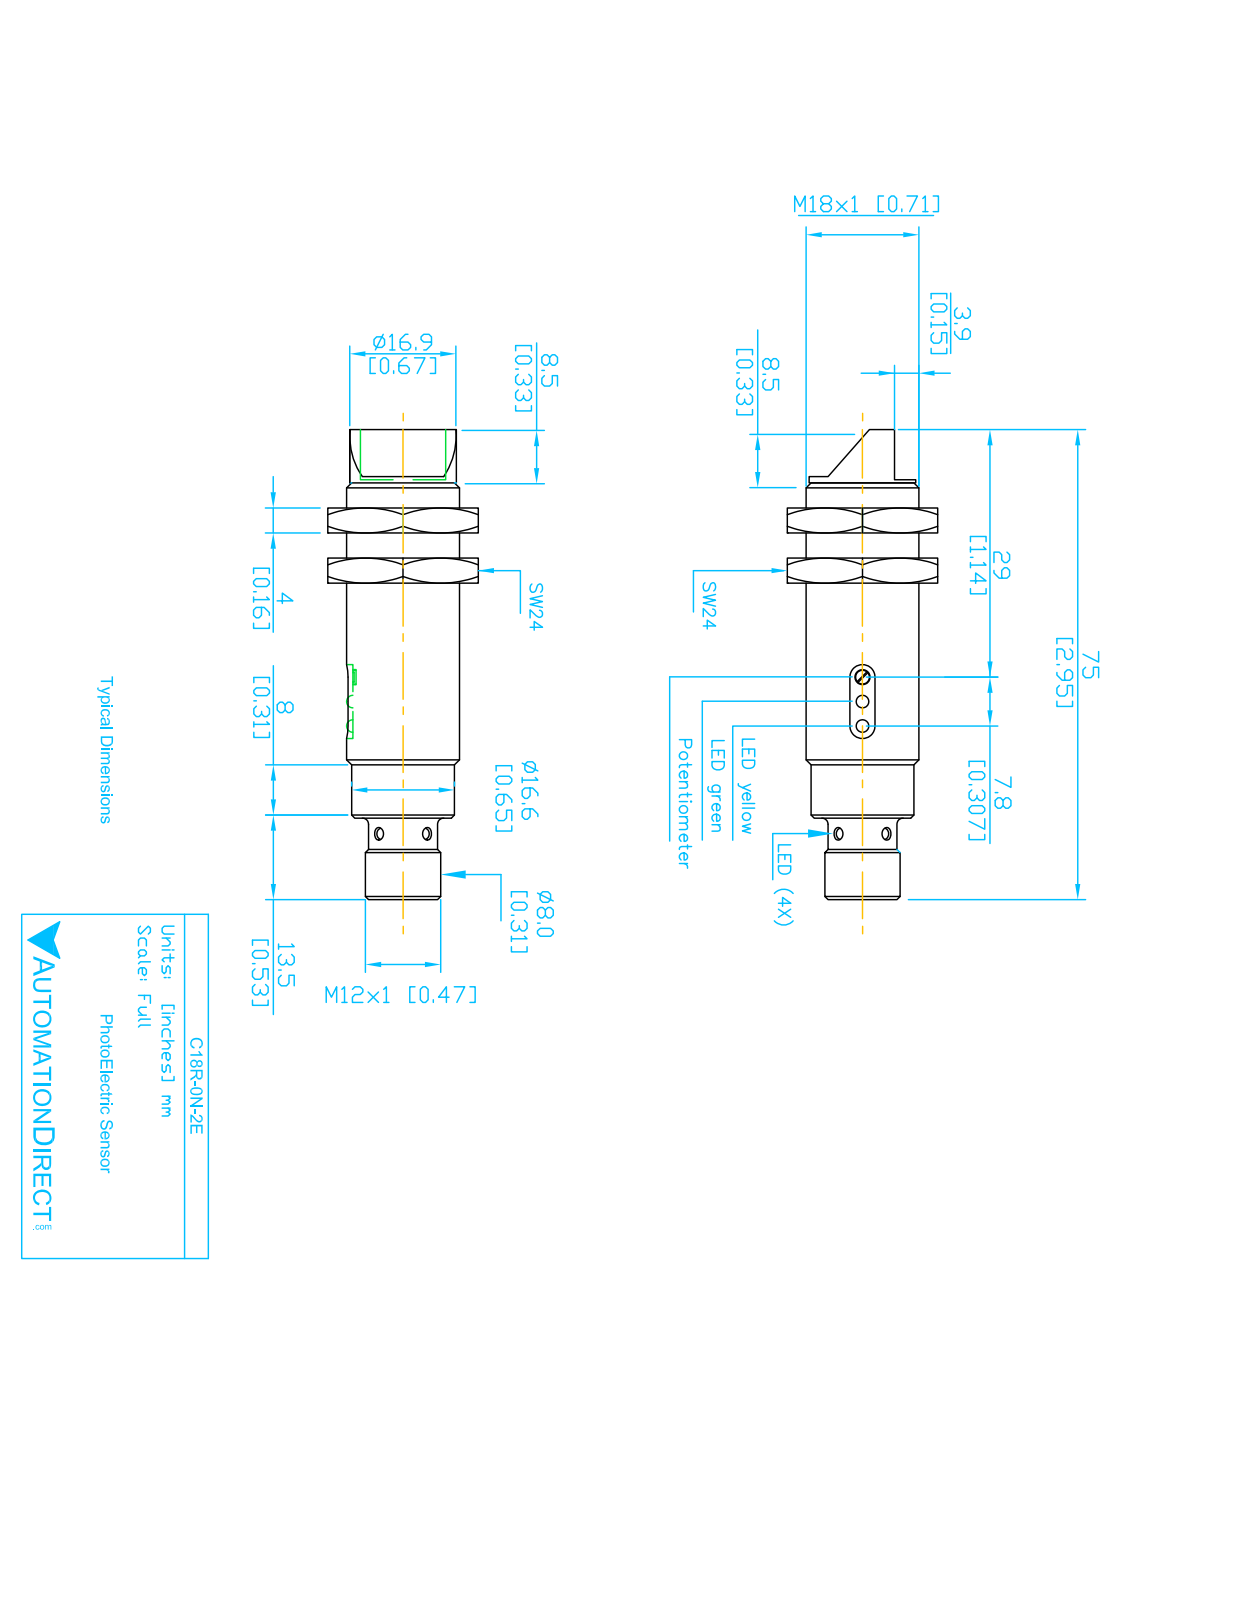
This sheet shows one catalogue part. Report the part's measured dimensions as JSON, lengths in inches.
{"part_name": "C18R-0N-2E", "step_written_by": "SolidWorks 2017 (AUTOMOTIVE_DESIGN)", "units": "inches", "bodies": {"solids": 2, "faces": 85, "planar": 18, "cylindrical": 35, "other": 32}, "overall_size": [2.957, 0.709, 0.709], "volume_in3": 0.905, "surface_area_in2": 7.969, "round_holes": [[0.118, 2], [0.335, 1]], "round_bosses_or_shafts": [[0.04, 4], [0.709, 1], [0.665, 1], [0.646, 1], [0.459, 1], [0.415, 1]], "partial_cylinders_radius": [[0.015, 6], [0.02, 2], [0.202, 1]], "face_to_face_distances": [0.169, 0.512, 0.343, 2.445, 2.614, 2.957, 0.28, 2.165, 2.335, 2.677]}
